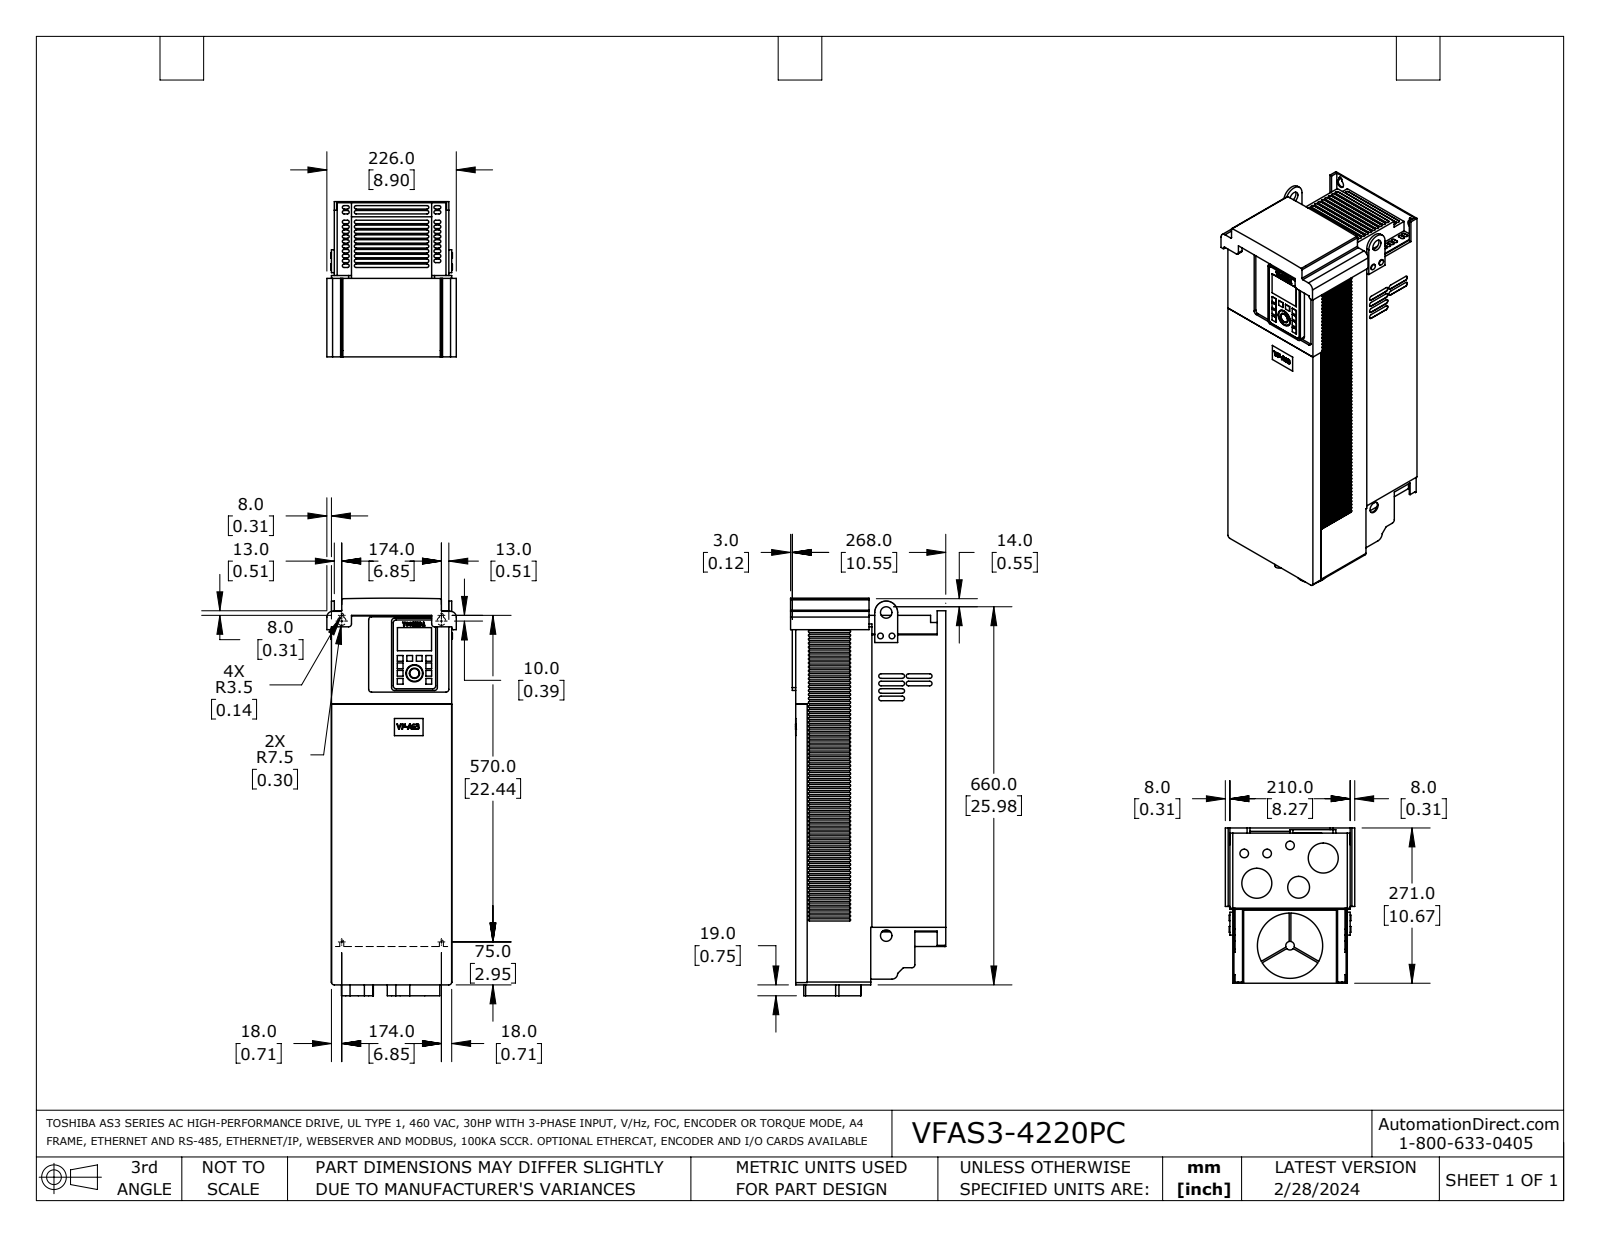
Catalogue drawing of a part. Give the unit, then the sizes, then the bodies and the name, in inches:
Units: inches
Overall size (bounding box): 27.323 × 10.669 × 8.898
Round holes (diameter × count): ⌀0.591 ×2, ⌀0.787 ×2, ⌀0.63 ×1, ⌀1.102 ×1, ⌀4.488 ×1
Round bosses / shafts (diameter × count): ⌀0.591 ×4, ⌀2.063 ×2, ⌀0.394 ×2, ⌀1.5 ×1, ⌀1.181 ×1, ⌀0.709 ×1
Partial cylindrical surfaces — rounded edges, fillets, slot ends (radius × count): R0.075 ×152, R0.118 ×72, R0.197 ×16, R0.157 ×12, R0.039 ×5, R0.078 ×5, R0.079 ×4, R0.138 ×4
Main face-to-face distances: 0.197, 10.315, 8.071, 7.874, 8.268, 0.187, 8.258, 8.061, 0.079, 5.079
Hole centre spacings: 4.036, 6.154, 6.85, 22.205
Volume: 2 022 in³ · Surface area: 1 353 in²
Bodies: 2 solids, 1636 faces (953 planar, 683 cylindrical, 0 other)
Part name (STEP PRODUCT): VFAS3-4220PC
STEP written by: SolidWorks 2021 (AUTOMOTIVE_DESIGN)
